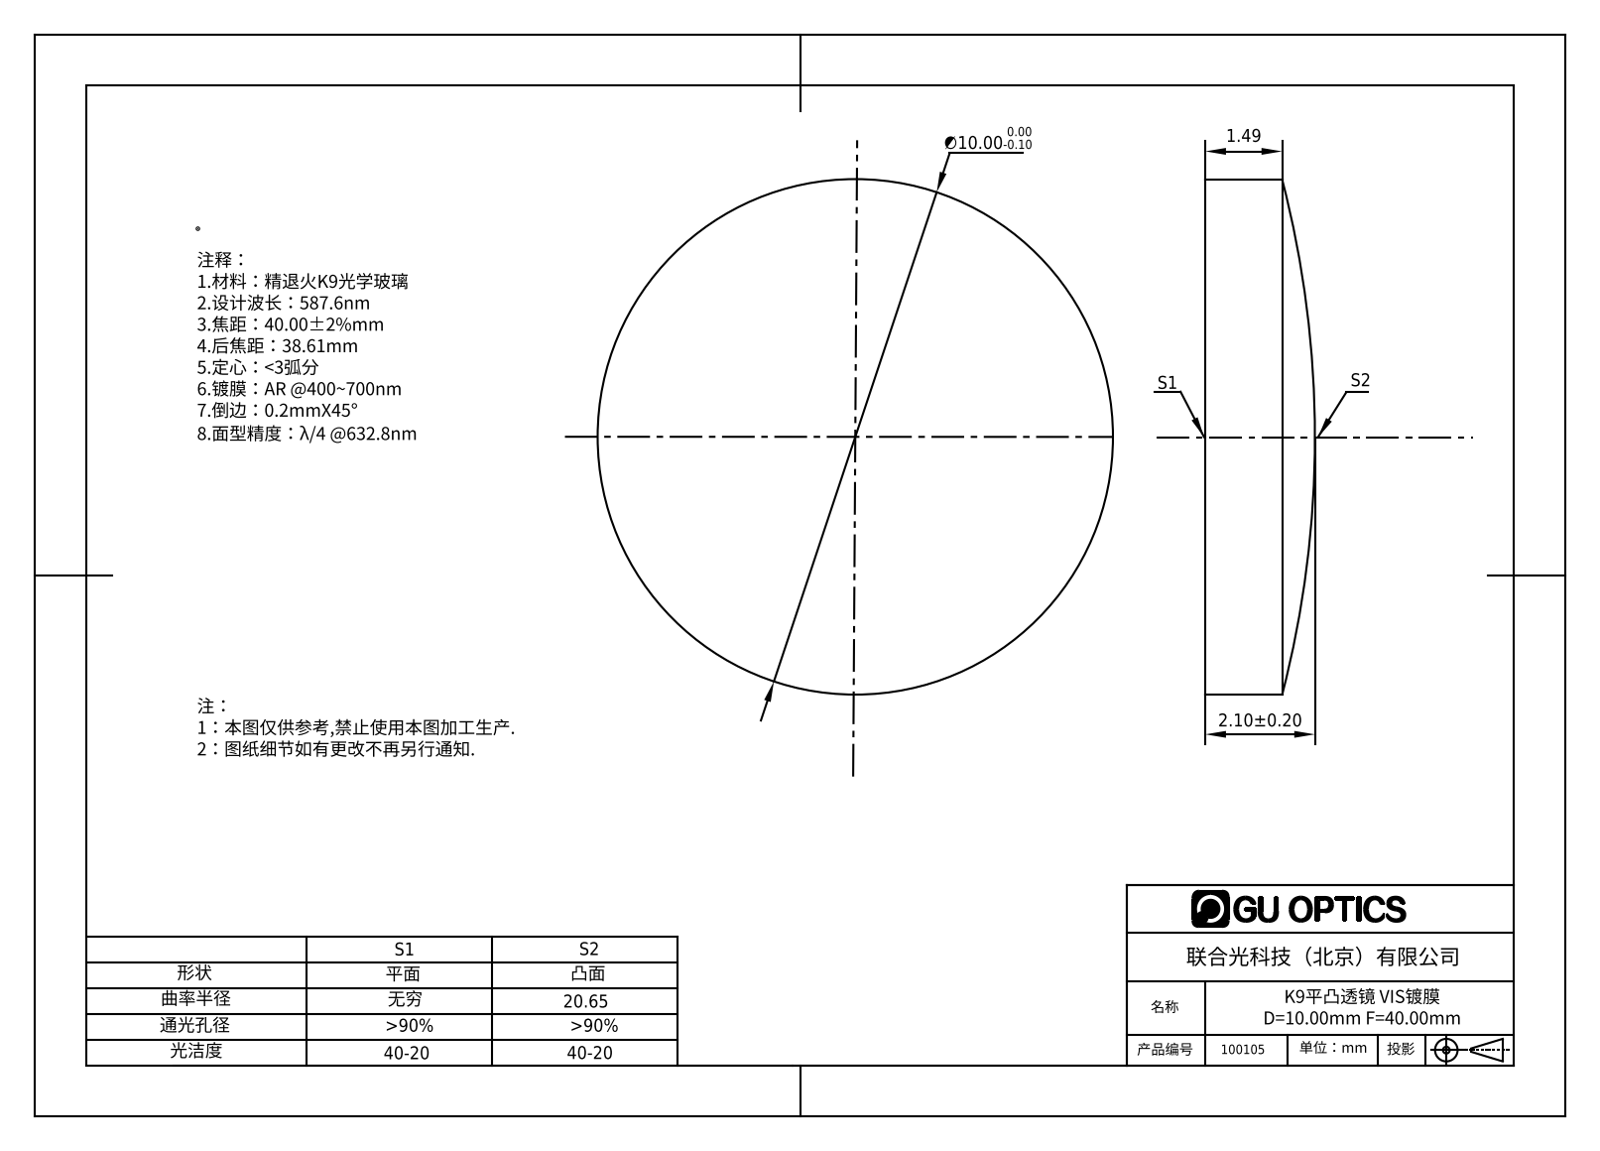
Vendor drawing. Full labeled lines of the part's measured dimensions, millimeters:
Part name (STEP PRODUCT): 100105
STEP written by: SolidWorks 2016 (AUTOMOTIVE_DESIGN)
Units: millimetres
Bodies: 1 solid, 5 faces (1 planar, 2 cylindrical, 2 other)
Overall size (bounding box): 10 × 10 × 2.13
Volume: 142 mm³ · Surface area: 205 mm²
Round bosses / shafts (diameter × count): ⌀10 ×1
